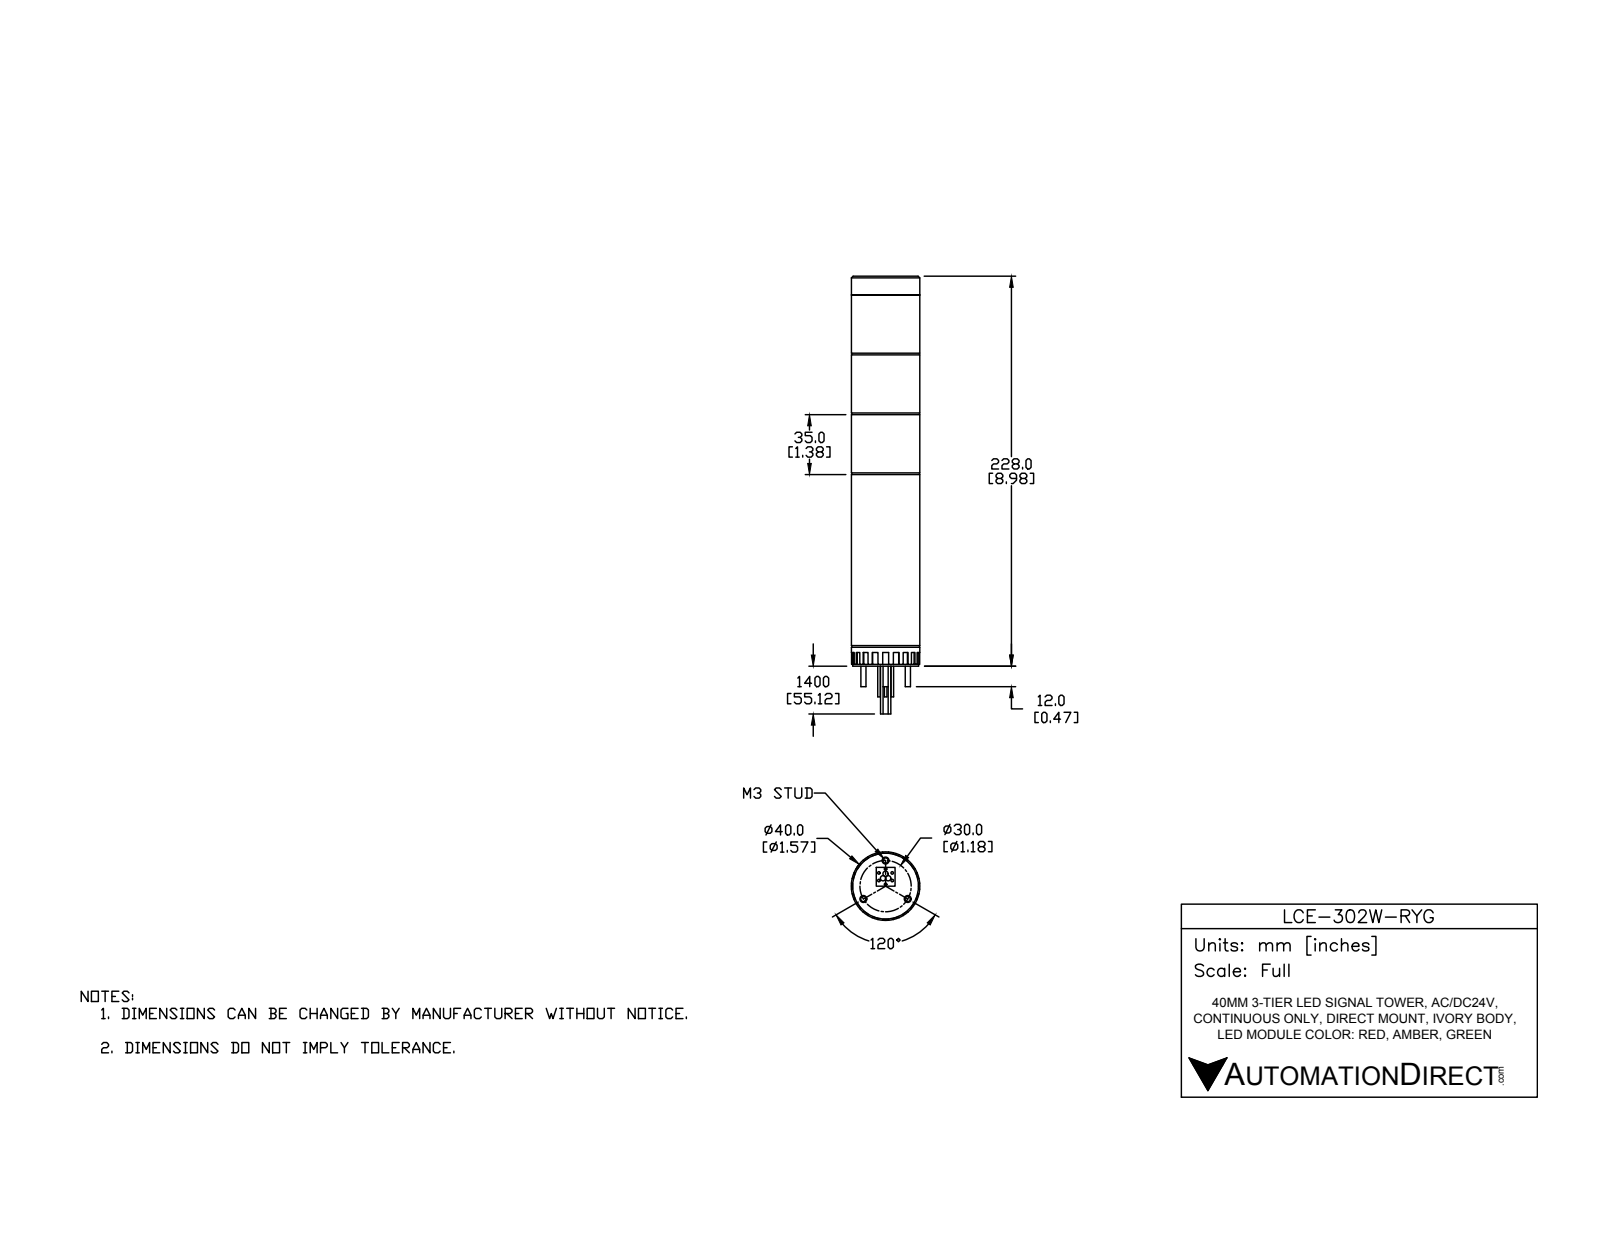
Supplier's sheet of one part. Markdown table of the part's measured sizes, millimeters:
| quantity | value |
| --- | --- |
| part name | LCE-302W-RYG |
| STEP written by | SolidWorks 2016 (AUTOMOTIVE_DESIGN) |
| units | millimeters |
| bodies | 21 solids, 202 faces (148 planar, 50 cylindrical, 4 other) |
| overall size | 246 × 40 × 40 |
| volume | 284 889 mm³ |
| surface area | 57 146 mm² |
| round holes (diameter × count) | 4 × 3, 8 × 1 |
| round bosses / shafts (diameter × count) | 1.5 × 6, 3 × 3, 40 × 1, 39.5 × 1, 38.5 × 1, 5.5 × 1 |
| main face-to-face distances | 35, 1, 70, 34, 36, 69, 101, 136, 171, 11 |
| hole center spacings | 15, 25.98 |
